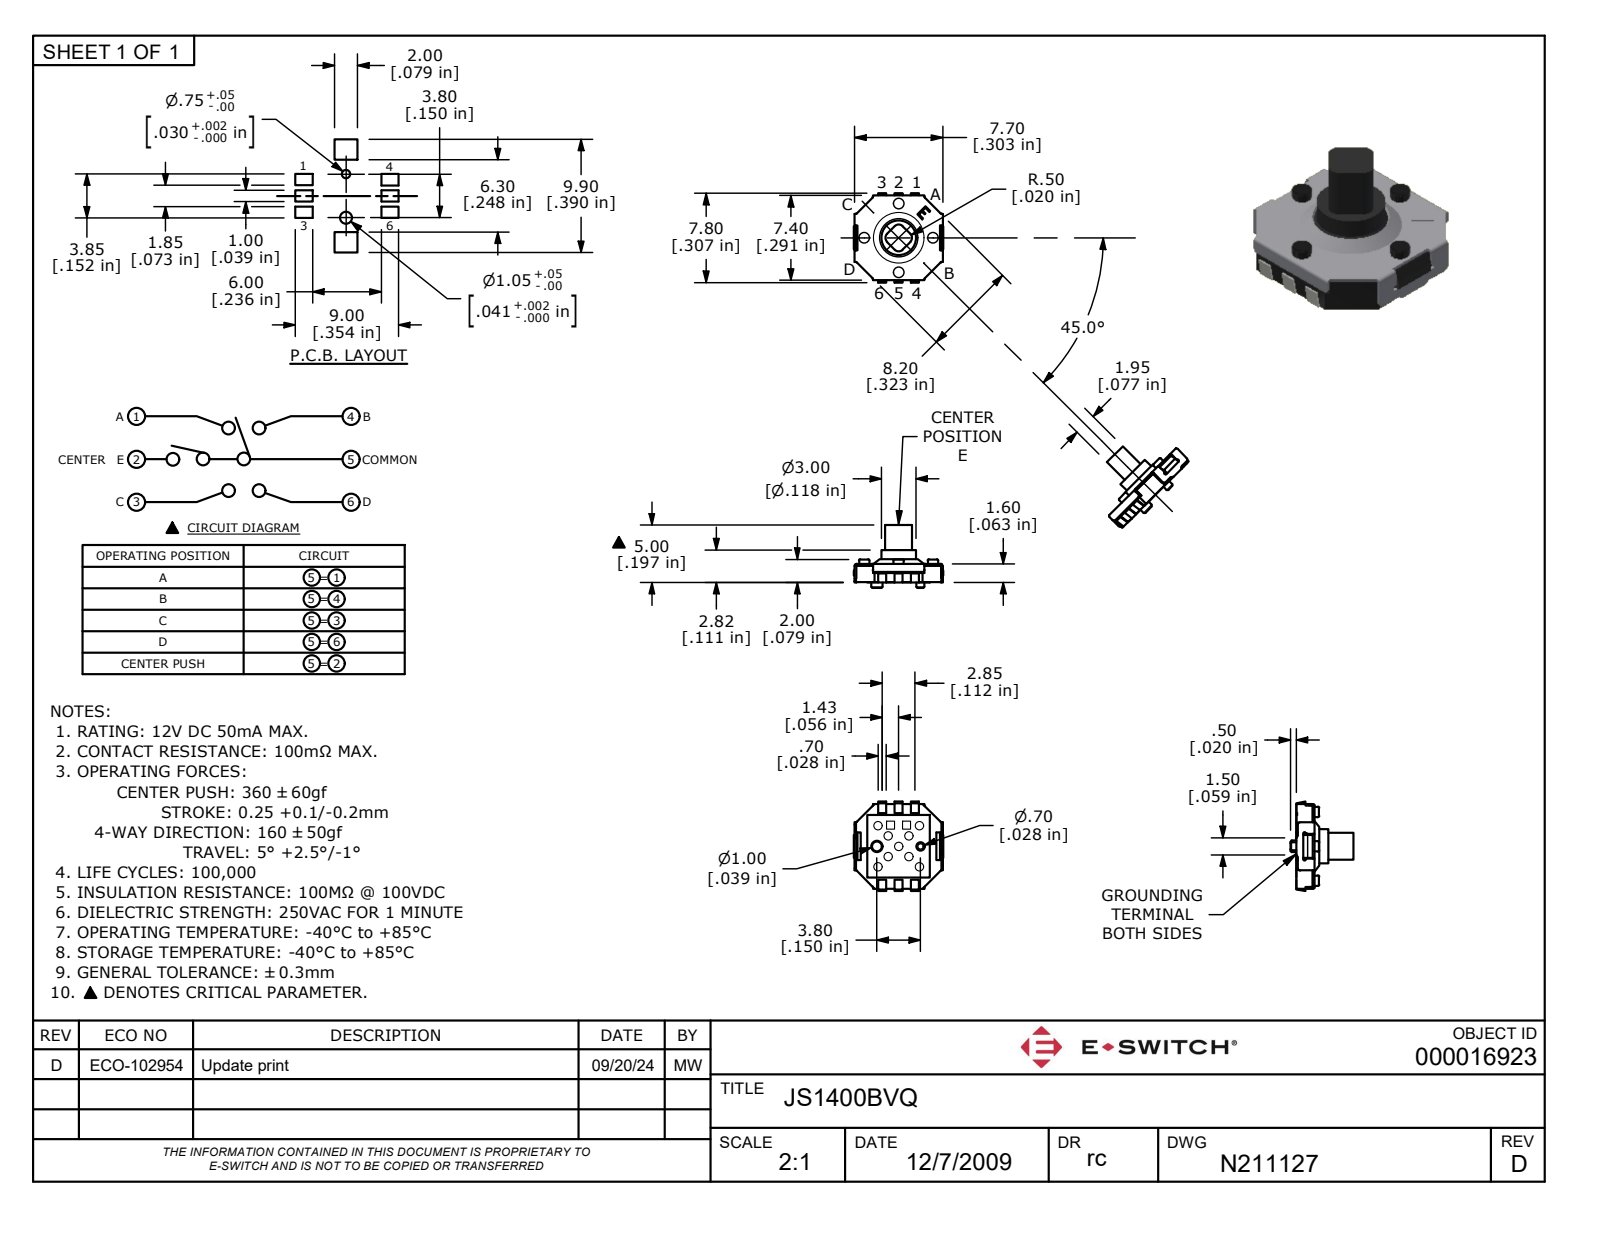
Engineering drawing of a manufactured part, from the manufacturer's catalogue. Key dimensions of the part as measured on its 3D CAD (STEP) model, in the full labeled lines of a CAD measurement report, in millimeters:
Part name (STEP PRODUCT): P:\\E-Switch Secure\\3D_MODELS_STP_FORMAT\\JS1400BVQ.stp
STEP written by: ACIS (CONFIG_CONTROL_DESIGN)
Units: millimetres
Bodies: 2 solids, 253 faces (199 planar, 44 cylindrical, 10 other)
Overall size (bounding box): 7.8 × 7.8 × 5.5
Volume: 80 mm³ · Surface area: 330 mm²
Round holes (diameter × count): ⌀0.7 ×9, ⌀0.8 ×4
Round bosses / shafts (diameter × count): ⌀0.7 ×5, ⌀0.9 ×4, ⌀3 ×1, ⌀1 ×1
Partial cylindrical surfaces — rounded edges, fillets, slot ends (radius × count): R0.5 ×4, R1.2 ×4
Main face-to-face distances: 0.6, 1, 1.6, 0.4, 0.9, 0.7, 1.4, 0.9, 0.5, 1.3
Hole centre spacings: 1.3, 2.2, 2.3, 2.8, 4, 5.1, 2.5, 1.8
